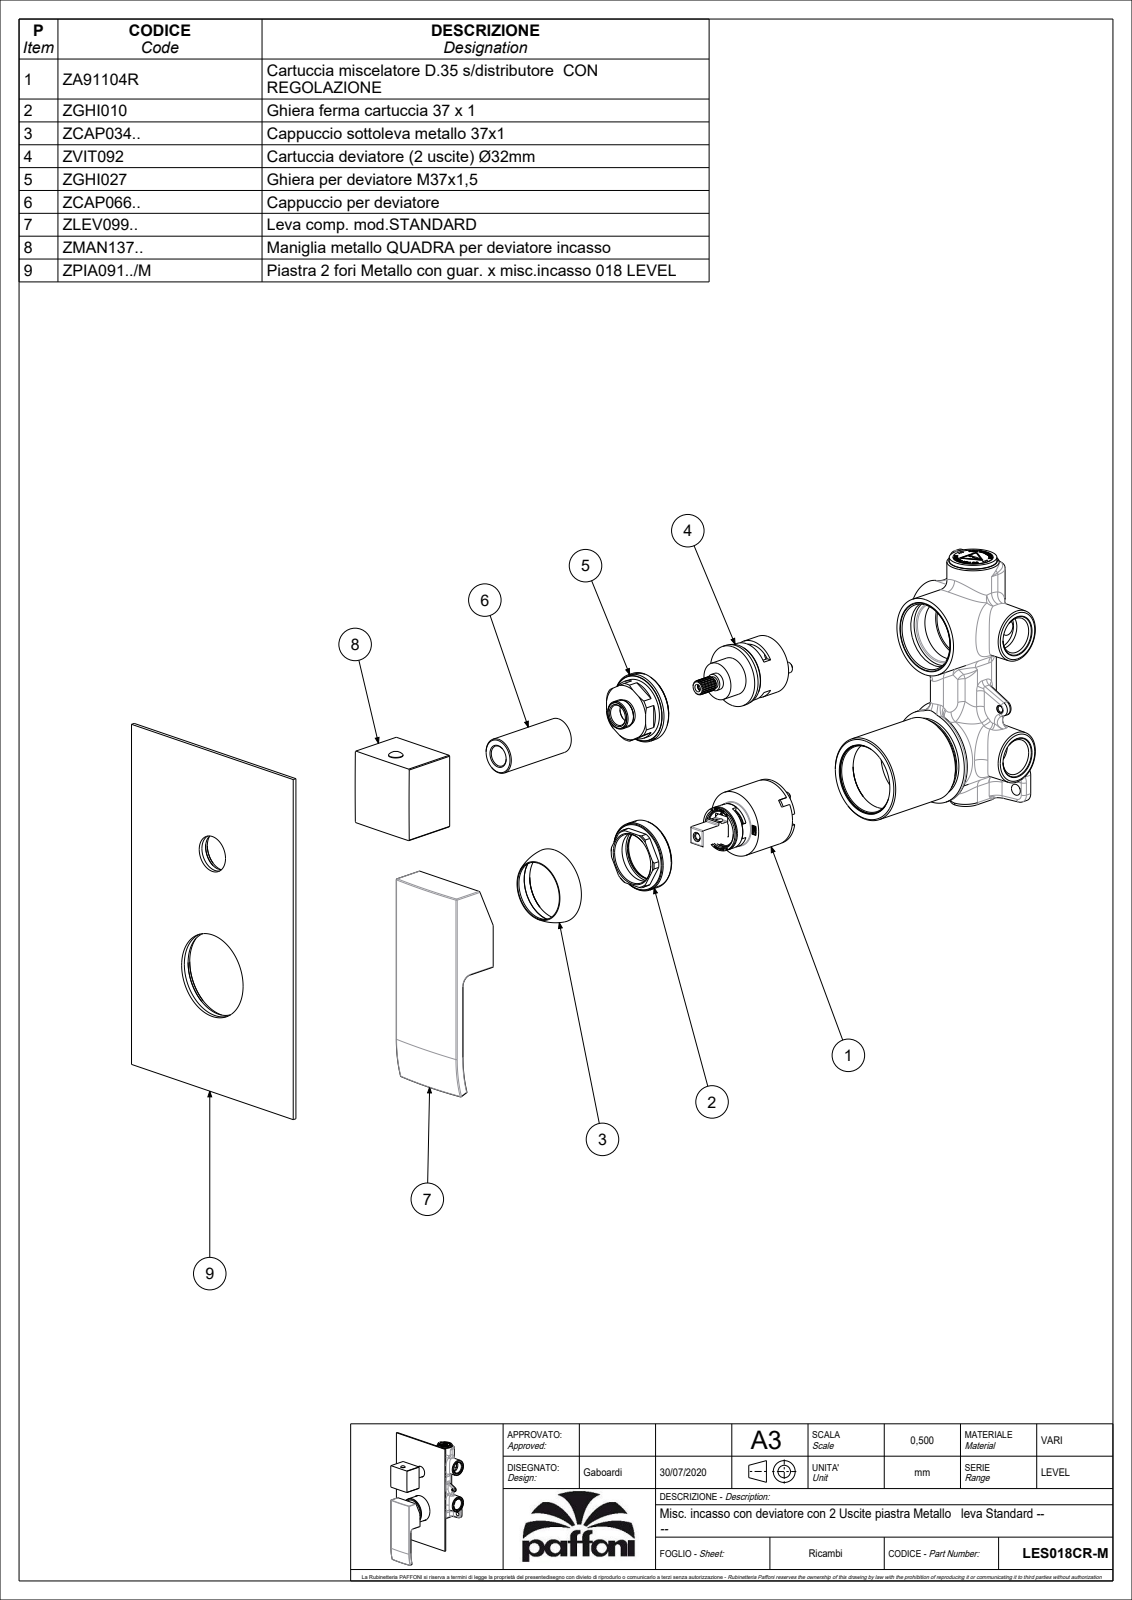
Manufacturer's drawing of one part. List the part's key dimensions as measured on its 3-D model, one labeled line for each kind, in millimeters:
Part name (STEP PRODUCT): LES018CR-M
STEP written by: CREO PARAMETRIC BY PTC INC, 2020044 (CONFIG_CONTROL_DESIGN)
Units: millimetres
Bodies: 4 solids, 1006 faces (583 planar, 254 cylindrical, 169 other)
Overall size (bounding box): 213.38 × 120 × 56.39
Volume: 138 489 mm³ · Surface area: 102 656 mm²
Round holes (diameter × count): ⌀3 ×2, ⌀4 ×2, ⌀5.5 ×2, ⌀19.5 ×2, ⌀36 ×2, ⌀3.2 ×1, ⌀3.3 ×1, ⌀4.2 ×1, ⌀4.5 ×1, ⌀5 ×1, ⌀7.8 ×1, ⌀11 ×1
Round bosses / shafts (diameter × count): ⌀7.6 ×2, ⌀44.8 ×1, ⌀35 ×1, ⌀25 ×1, ⌀23.5 ×1, ⌀23.4 ×1, ⌀21.8 ×1, ⌀18.7 ×1
Partial cylindrical surfaces — rounded edges, fillets, slot ends (radius × count): R1.5 ×14, R0.5 ×12, R0.15 ×11, R0.3 ×4, R2 ×4, R1 ×2, R300 ×2, R2.25 ×1
Main face-to-face distances: 2, 40, 2.5, 42.5, 45, 51.3, 49.3, 15.5, 37.5, 80
Hole centre spacings: 6.8, 8, 10, 14.8, 58, 68
